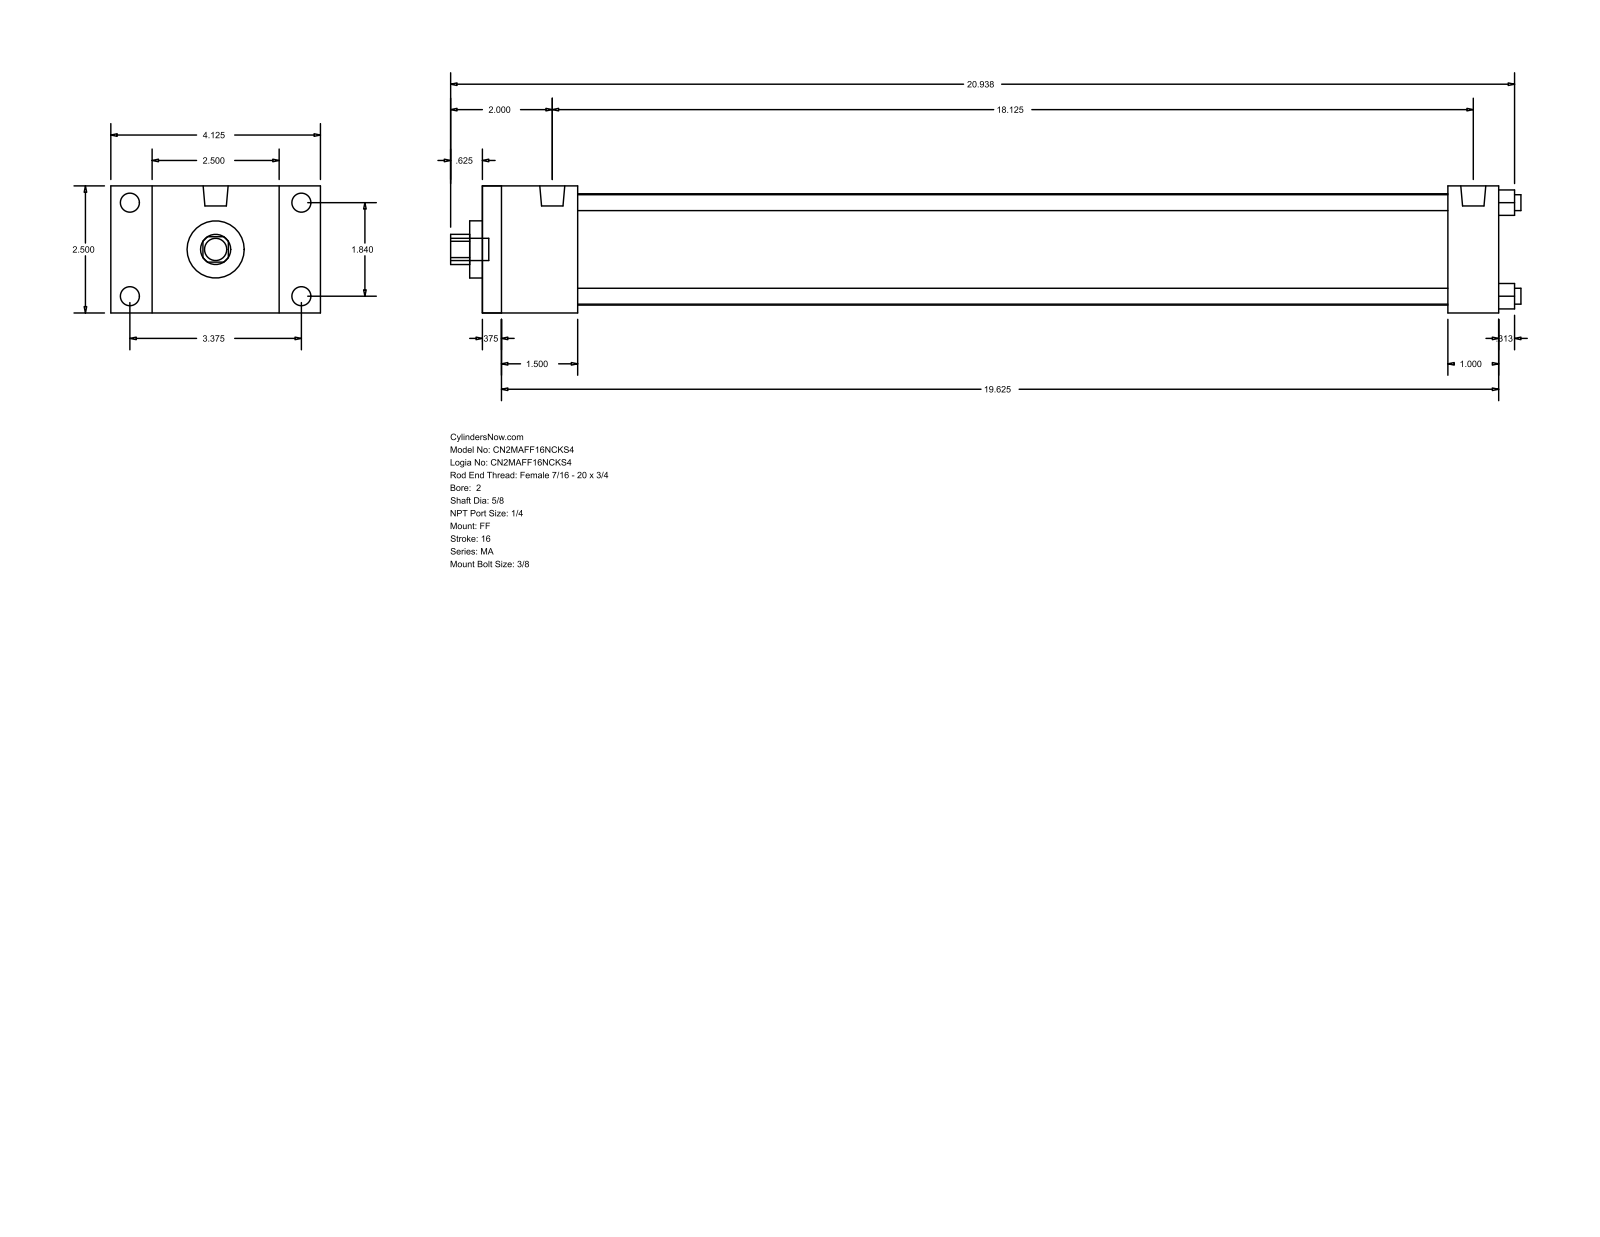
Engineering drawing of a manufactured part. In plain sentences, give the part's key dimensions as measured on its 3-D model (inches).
The part is named "MA_FF__0200_0.625". Its 3-D file was written by "GSSL Pune (CONFIG_CONTROL_DESIGN)". It is 0 solids with 92 faces: 64 planar, 28 cylindrical and 0 other. Overall it measures 21.063 by 4.125 by 2.5 inches. Round holes: 4 of diameter 0.313, 1 of diameter 0.625, 1 of diameter 1.125, 1 of diameter 2.19. Round bosses or shafts: 4 of diameter 0.375, 4 of diameter 0.313, 2 of diameter 0.492, 1 of diameter 0.437. Partial cylindrical surfaces (rounded edges, fillets, slot ends): 1 of radius 0.297. The main face-to-face distances are 2.5, 20, 0.375, 19.625, 1, 1.5, 1.875, 19, 18.625, 17.125. The hole center spacings are 1.301, 1.84, 2.602.
